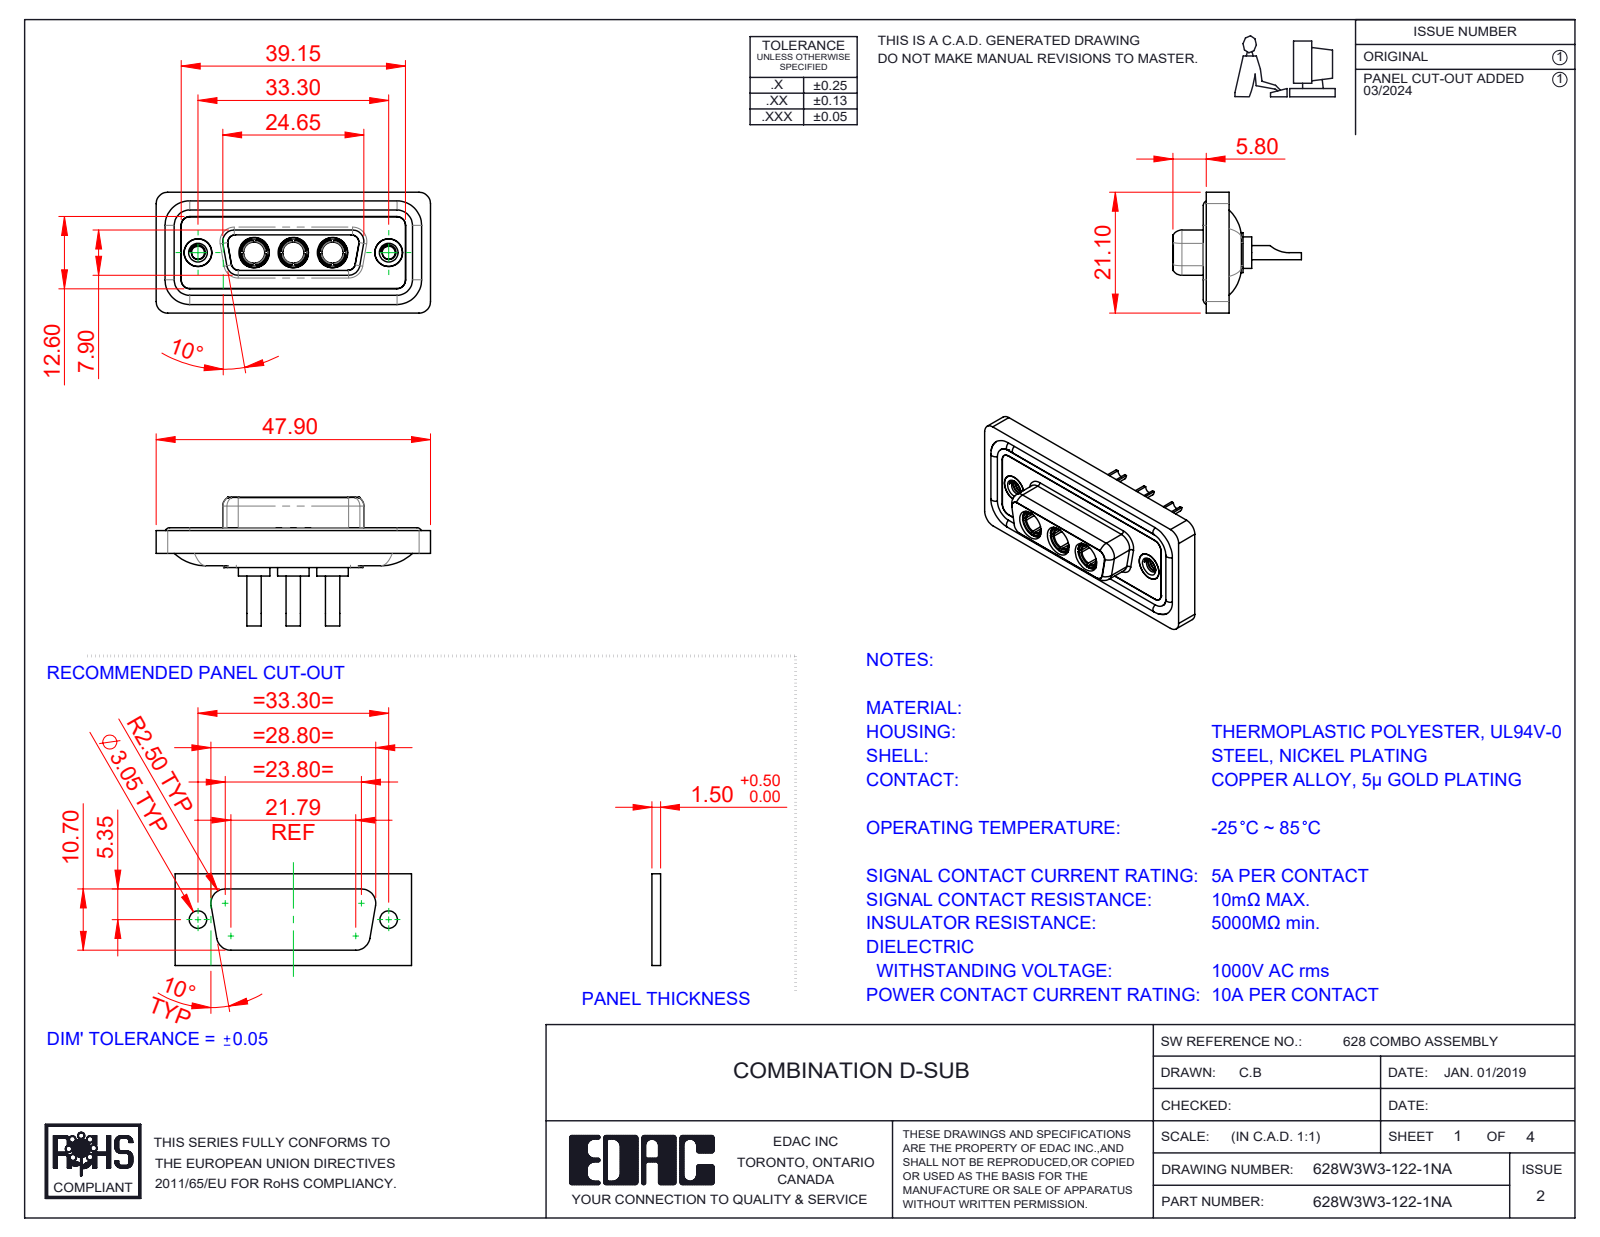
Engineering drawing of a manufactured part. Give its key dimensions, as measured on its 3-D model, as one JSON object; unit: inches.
{"part_name": "628Combo Threaded Rivet_A; 628Combo Shell Rear_15 Contacts; 628Combo Shell Front_15 Contacts; 628Combo Waterproof Housing_15 Contacts (+3 more)", "step_written_by": "SolidWorks 2023 (CONFIG_CONTROL_DESIGN)", "units": "inches", "bodies": {"solids": 13, "faces": 621, "planar": 198, "cylindrical": 268, "other": 155}, "overall_size": [1.886, 0.884, 0.831], "volume_in3": 0.367, "surface_area_in2": 15.31, "round_holes": [[0.191, 5], [0.067, 3], [0.146, 3], [0.209, 3], [0.089, 2], [0.157, 2], [0.159, 2], [0.197, 2]], "round_bosses_or_shafts": [[0.063, 4], [0.217, 3], [0.205, 3], [0.195, 3], [0.187, 3], [0.148, 3], [0.098, 3], [0.195, 2]], "partial_cylinders_radius": [[0.059, 22], [0.079, 20], [0.053, 12], [0.063, 8], [0.01, 4], [0.02, 4], [0.024, 4], [0.026, 4]], "face_to_face_distances": [0.016, 0.071, 0.063, 0.02, 0.293, 0.043, 0.114, 0.222, 0.278, 0.26], "hole_center_spacings": [0.27, 0.386, 0.656, 0.925, 0.539, 1.311]}
